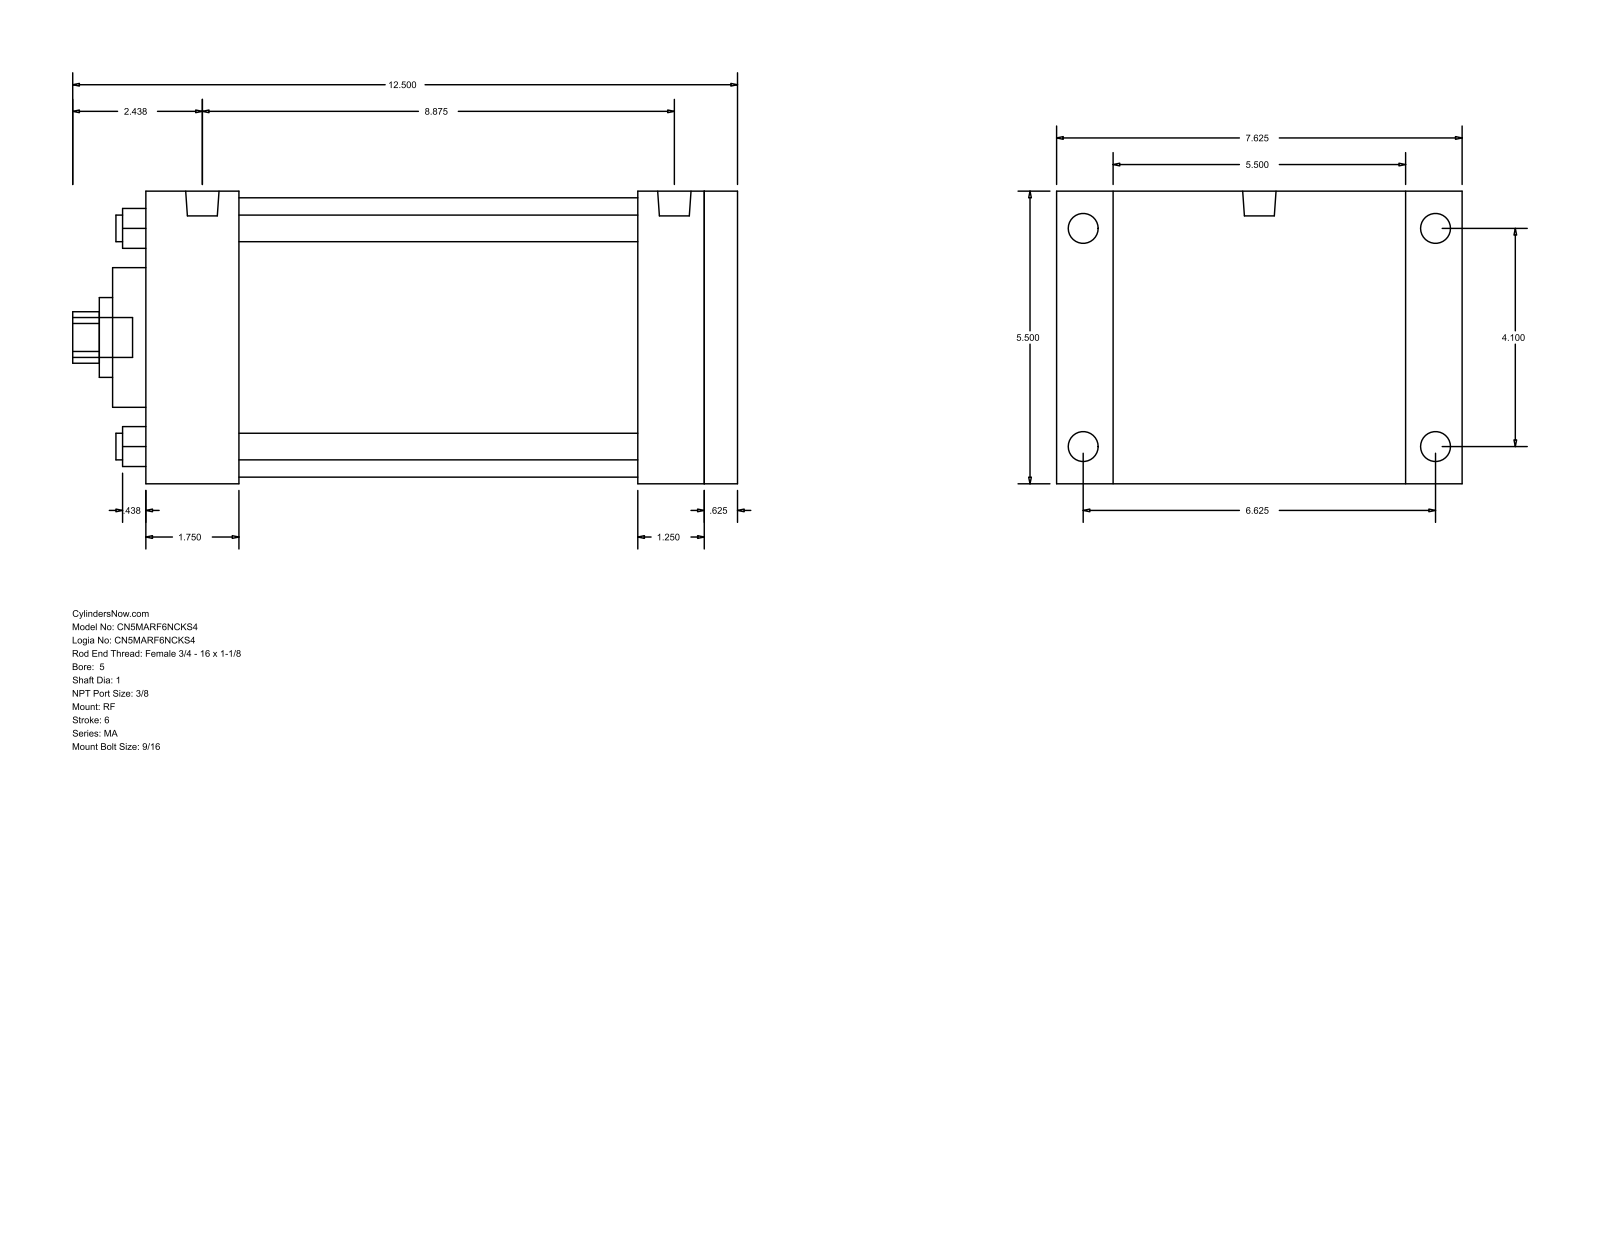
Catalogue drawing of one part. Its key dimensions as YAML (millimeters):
part_name: "MA_RF__0500_1"
step_written_by: "GSSL Pune (CONFIG_CONTROL_DESIGN)"
units: millimeters
bodies: {solids: 0, faces: 94, planar: 65, cylindrical: 29, other: 0}
overall_size: [317.5, 193.68, 139.7]
round_holes:
  - {diameter: 12.7, count: 4}
  - {diameter: 25.4, count: 1}
  - {diameter: 38.1, count: 1}
  - {diameter: 66.67, count: 1}
  - {diameter: 133.35, count: 1}
round_bosses_or_shafts:
  - {diameter: 14.29, count: 4}
  - {diameter: 11.11, count: 4}
  - {diameter: 15.93, count: 2}
  - {diameter: 19.05, count: 1}
partial_cylinders:
  - {radius: 12.29, count: 1}
face_to_face_distances: [139.7, 282.58, 266.7, 15.88, 44.46, 222.24, 238.12, 234.96, 190.5, 31.74]
hole_center_spacings: [73.64, 104.14, 147.28]
